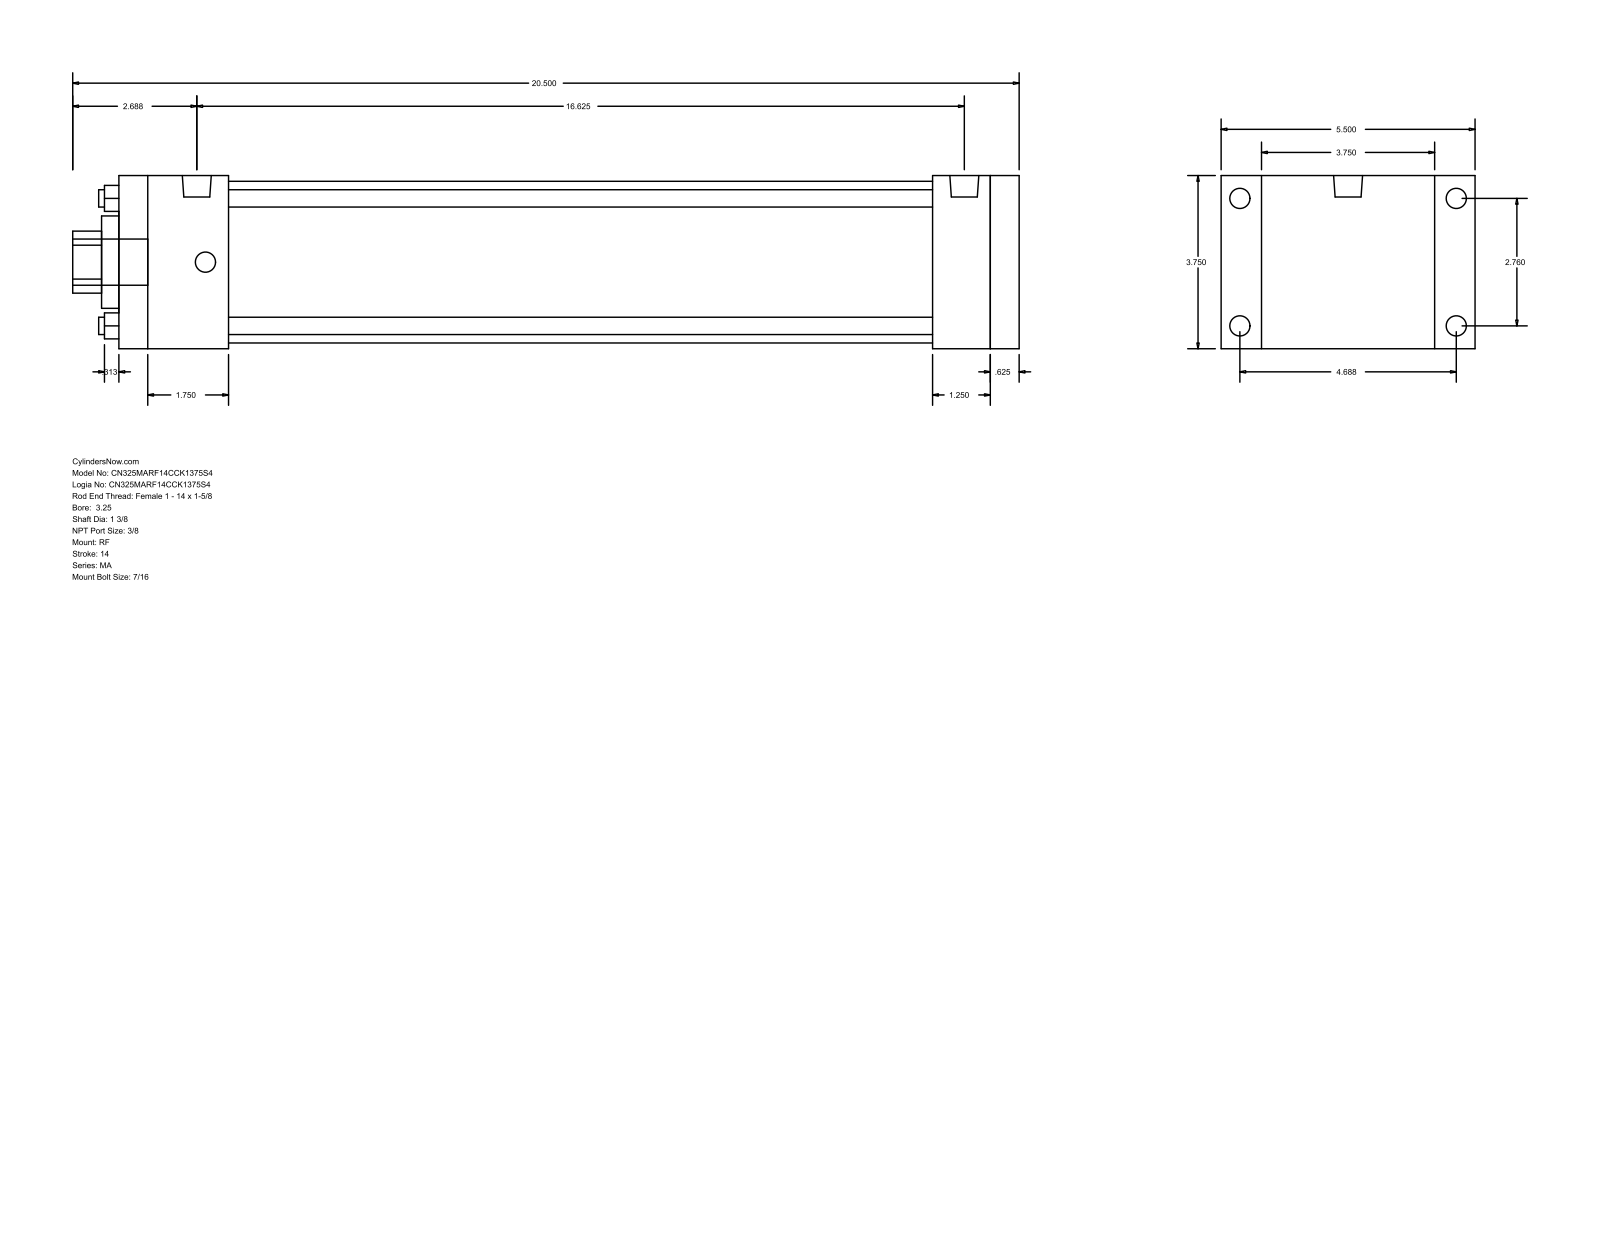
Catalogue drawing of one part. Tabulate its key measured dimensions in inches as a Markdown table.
| quantity | value |
| --- | --- |
| part name | MA_RF__0325_1.375 |
| STEP written by | GSSL Pune (CONFIG_CONTROL_DESIGN) |
| units | inches |
| bodies | 0 solids, 92 faces (64 planar, 28 cylindrical, 0 other) |
| overall size | 20.5 × 5.5 × 3.75 |
| round holes (diameter × count) | 0.375 × 4, 1.375 × 1, 2 × 1, 3.5 × 1 |
| round bosses / shafts (diameter × count) | 0.437 × 8, 0.627 × 2, 1 × 1 |
| partial cylindrical surfaces (radius × count) | 0.672 × 1 |
| main face-to-face distances | 3.75, 19.5, 0.625, 18.875, 0.875, 4.625, 17.625, 1.25, 1.875, 2.375 |
| hole center spacings | 1.952, 2.76, 3.903 |
